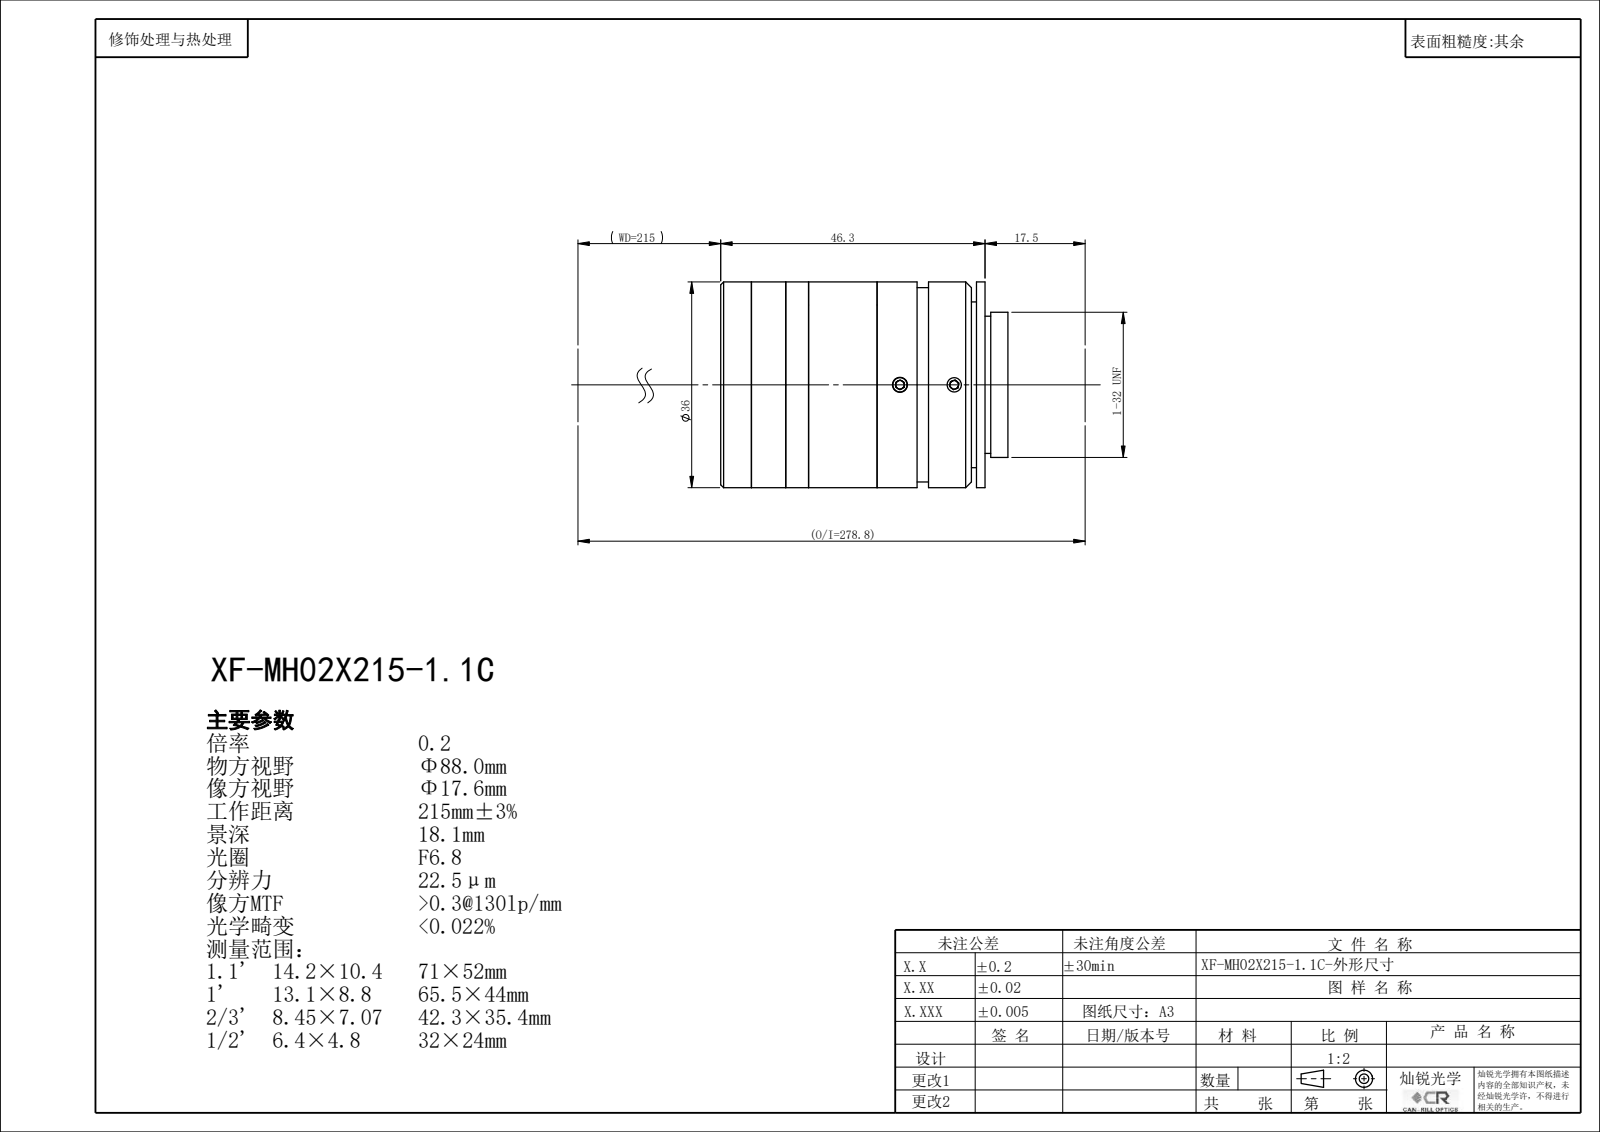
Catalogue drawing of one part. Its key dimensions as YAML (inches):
part_name: "XF-MH02X215-1.1C"
step_written_by: "SolidWorks 2022 (CONFIG_CONTROL_DESIGN)"
units: inches
bodies: {solids: 0, faces: 138, planar: 72, cylindrical: 40, other: 26}
overall_size: [1.979, 1.417, 1.417]
round_holes:
  - {diameter: 0.098, count: 3}
  - {diameter: 0.591, count: 1}
  - {diameter: 0.685, count: 1}
  - {diameter: 0.882, count: 1}
  - {diameter: 0.945, count: 1}
  - {diameter: 0.98, count: 1}
  - {diameter: 1.024, count: 1}
  - {diameter: 1.039, count: 1}
round_bosses_or_shafts:
  - {diameter: 1.417, count: 1}
  - {diameter: 1.339, count: 1}
  - {diameter: 1, count: 1}
face_to_face_distances: [0.744, 1.078, 1.822, 0.059, 1.763, 0.685, 0.606, 0.472, 1.157, 1.216]
